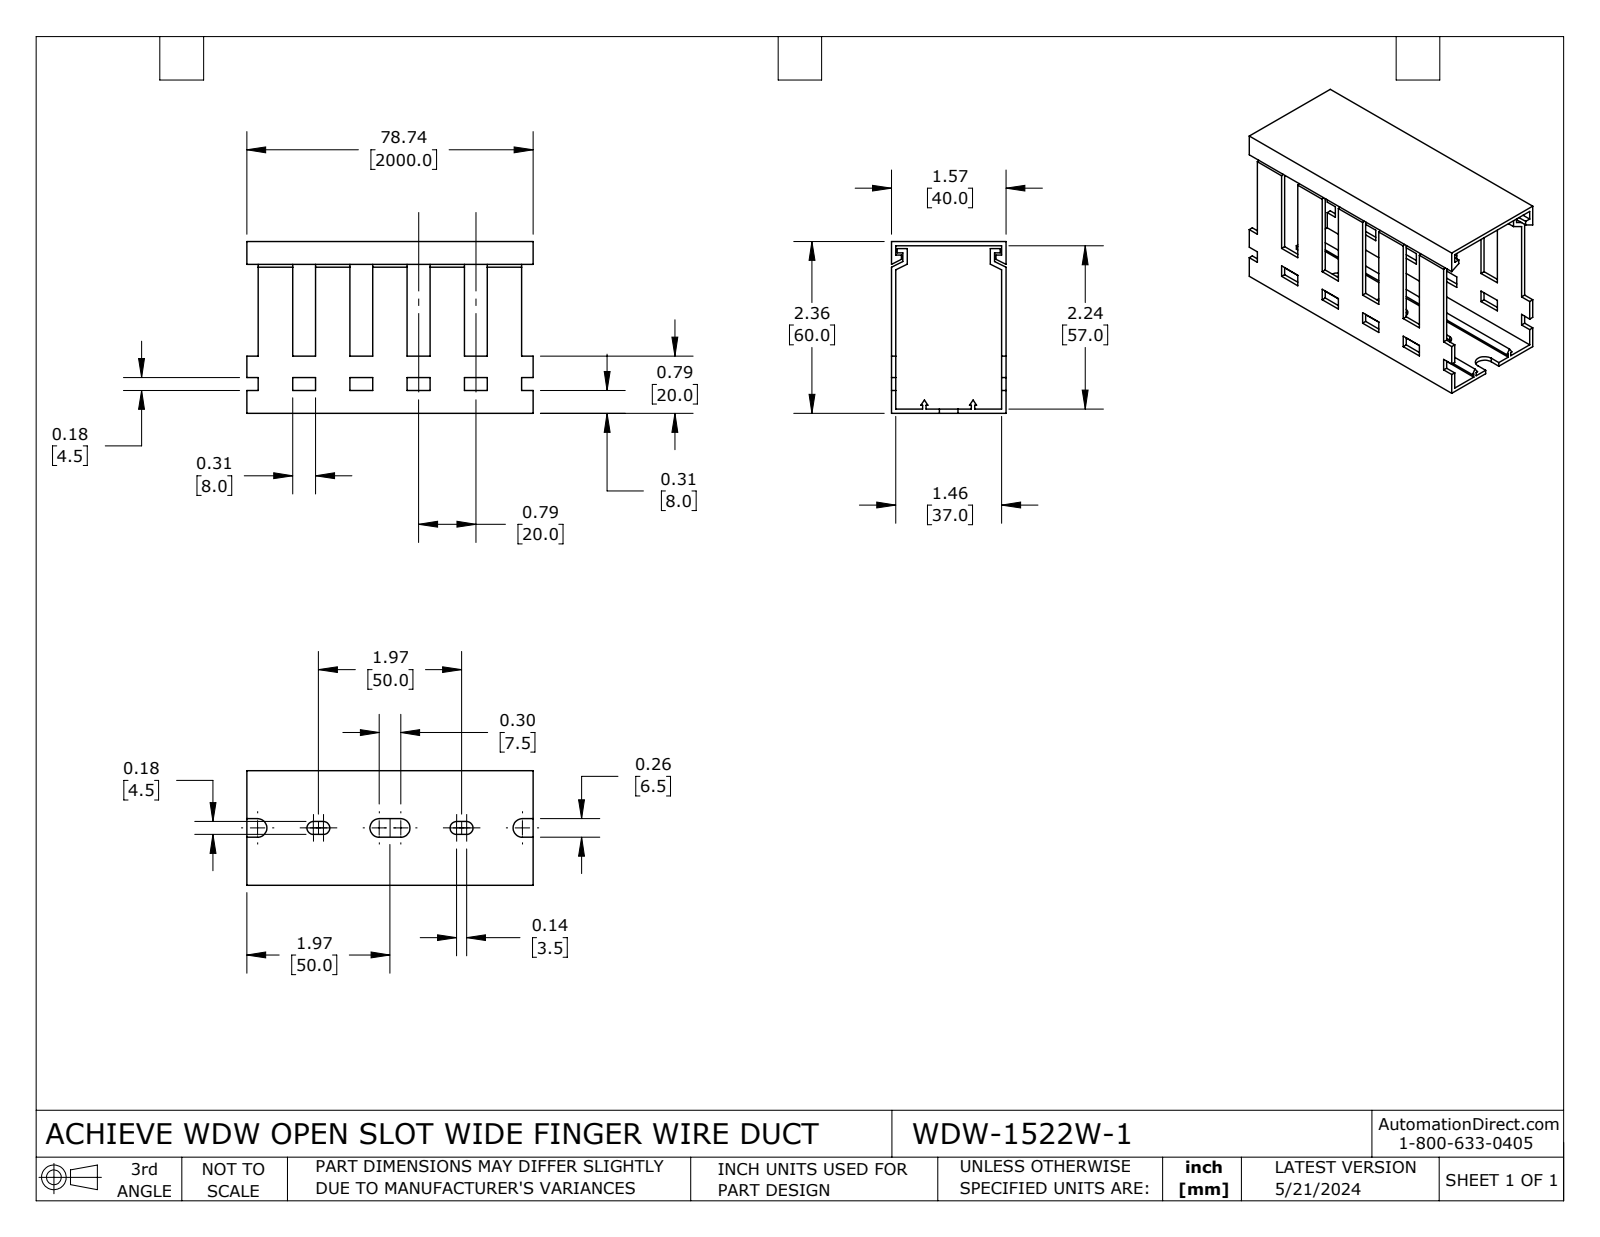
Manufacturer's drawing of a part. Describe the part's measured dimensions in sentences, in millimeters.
The part is named "WDW-1522W-1". Its 3-D file was written by "SolidWorks 2023 (CONFIG_CONTROL_DESIGN)". It is 2 solids with 210 faces: 198 planar, 12 cylindrical and 0 other. Overall it measures 100 by 60 by 40 millimeters. Its volume is 27 633 cubic millimeters and its surface area 39 639 square millimeters. Partial cylindrical surfaces (rounded edges, fillets, slot ends): 4 of radius 2.25, 4 of radius 3.25. The main face-to-face distances are 1.5, 38.5, 58.5, 40, 60, 37, 57, 4, 20, 34.5.
